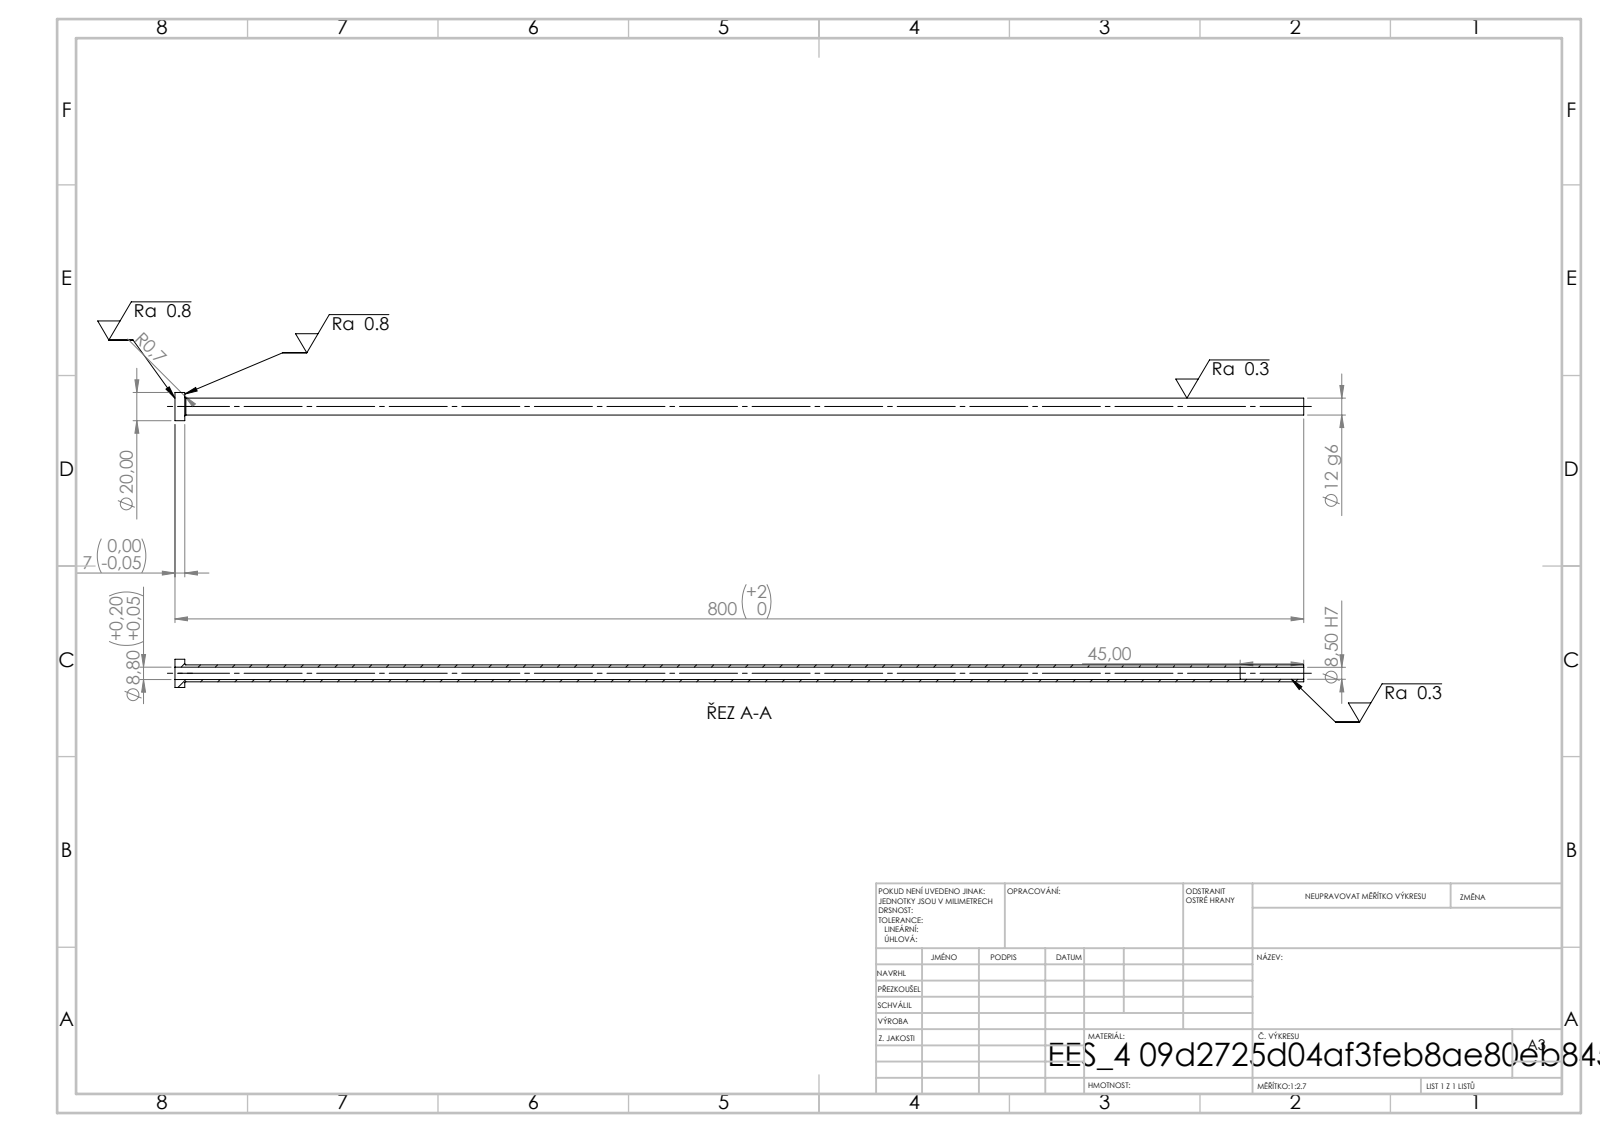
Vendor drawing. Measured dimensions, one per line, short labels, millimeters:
written by: SolidWorks 2019 (CONFIG_CONTROL_DESIGN)
unit: mm
bodies: 1 solid, 14 faces (4 planar, 8 cylindrical, 2 other)
size: 800 × 20 × 20
volume: 43 416 mm³; area: 52 913 mm²
holes: 1× ⌀8.5, 1× ⌀8.8
bosses: 1× ⌀20, 1× ⌀12
face distances: 7, 800, 793, 755, 748, 45
